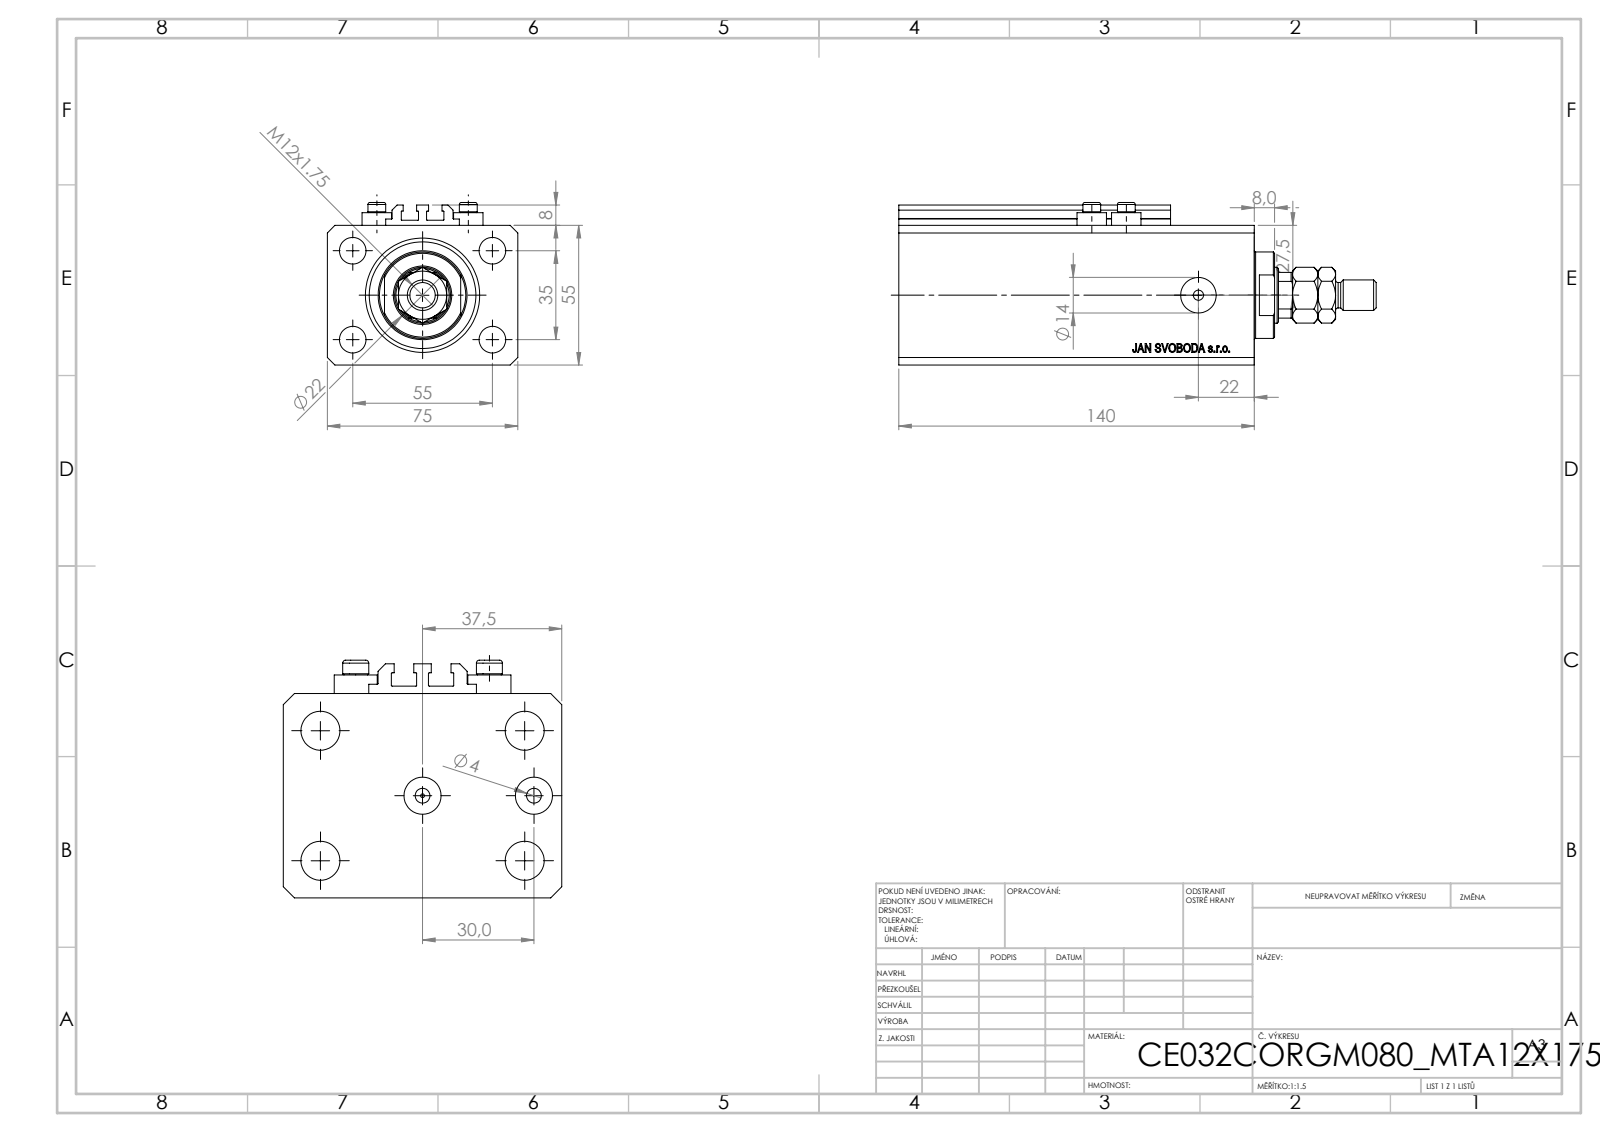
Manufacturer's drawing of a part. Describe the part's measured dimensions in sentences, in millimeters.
The part is named "V250CE_C_VCP; ALLEN BOLT V250CE; MTA; V250CE_C_Body (+1 more)". Its 3-D file was written by "SolidWorks 2019 (CONFIG_CONTROL_DESIGN)". It is 9 solids with 1087 faces: 519 planar, 92 cylindrical and 476 other. Overall it measures 187.9 by 75 by 64 millimeters. Its volume is 519 347 cubic millimeters and its surface area 116 158 square millimeters. Round holes: 8 of diameter 4, 5 of diameter 10.5, 2 of diameter 10, 2 of diameter 14, 1 of diameter 1.25, 1 of diameter 22, 1 of diameter 32, 1 of diameter 45. Round bosses or shafts: 4 of diameter 11.6, 4 of diameter 7, 1 of diameter 34, 1 of diameter 12. Partial cylindrical surfaces (rounded edges, fillets, slot ends): 10 of radius 0.2, 1 of radius 10.5. The main face-to-face distances are 55, 75, 140, 112.9, 27.1, 2.5, 9.9, 103, 130.1, 8. The hole center spacings are 32.6, 13.6, 17.68, 35, 36, 38.48, 55, 60.1.
